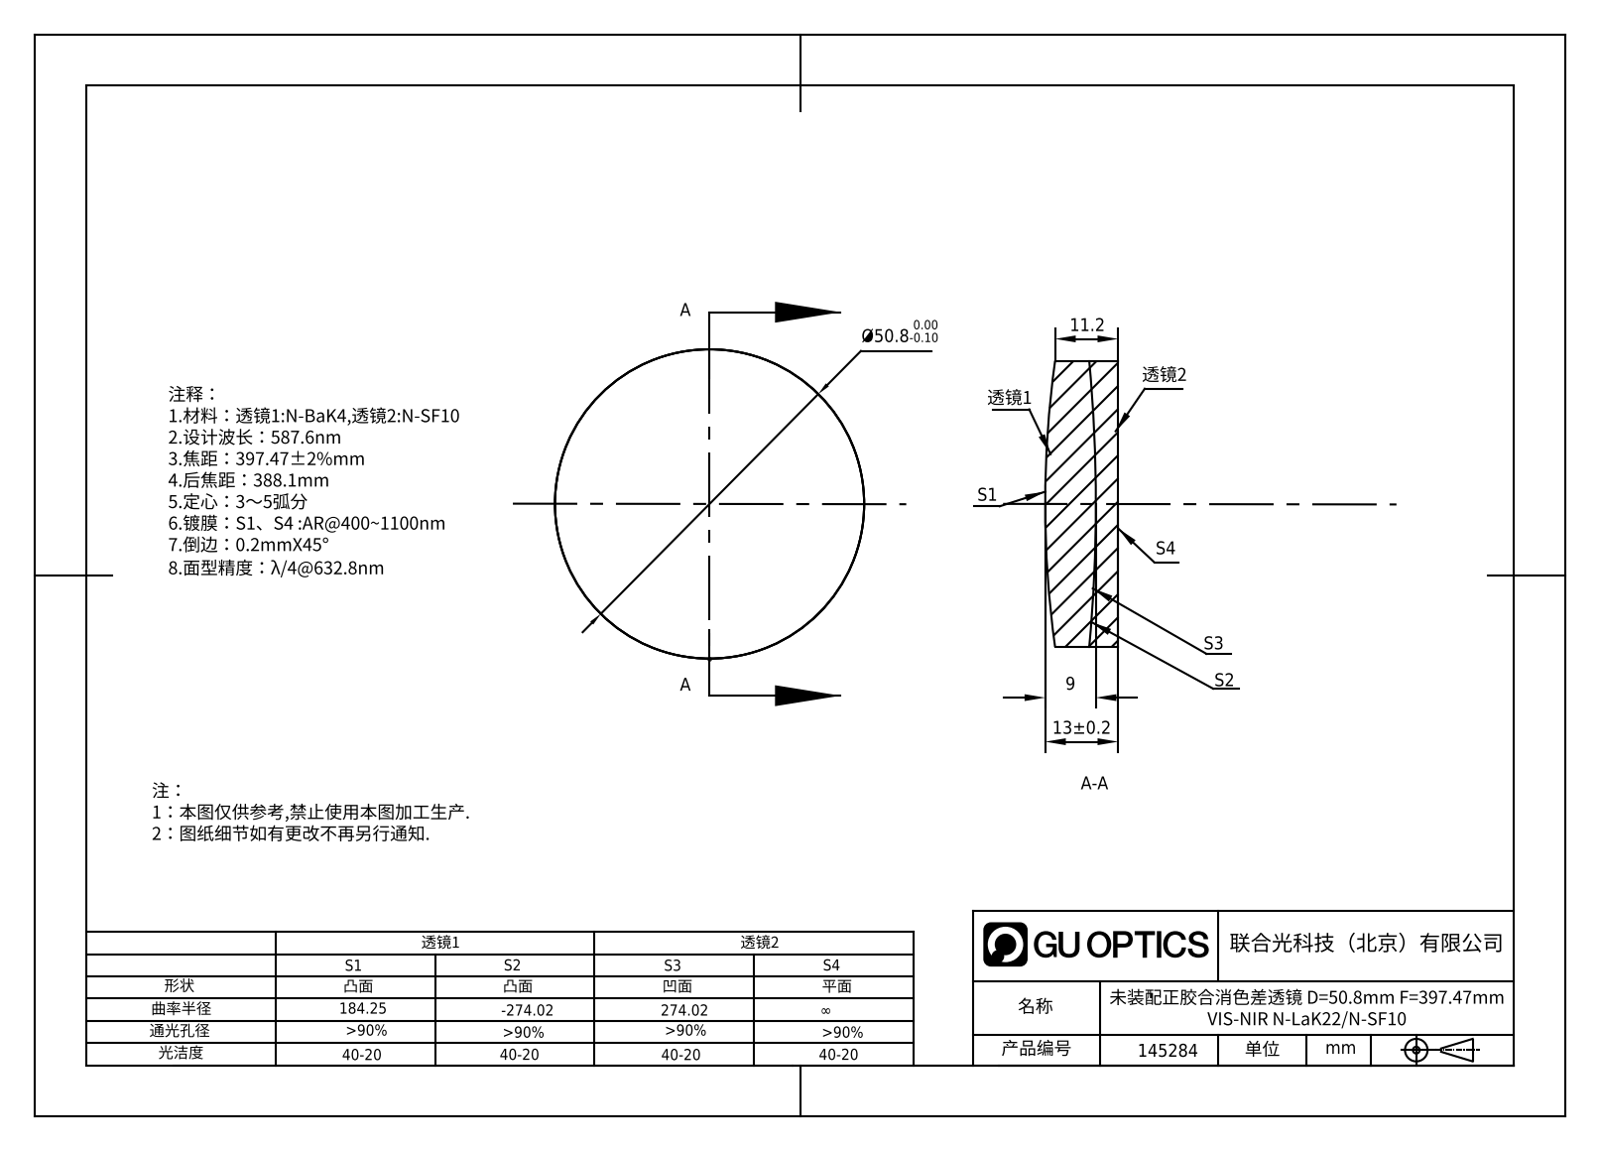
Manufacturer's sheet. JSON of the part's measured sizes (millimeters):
{"part_name": "145284", "step_written_by": "SolidWorks 2020 (CONFIG_CONTROL_DESIGN)", "units": "millimeters", "bodies": {"solids": 2, "faces": 11, "planar": 1, "cylindrical": 4, "other": 6}, "overall_size": [50.8, 50.8, 12.41], "volume_mm3": 23971, "surface_area_mm2": 9822, "round_bosses_or_shafts": [[50.8, 1]]}
